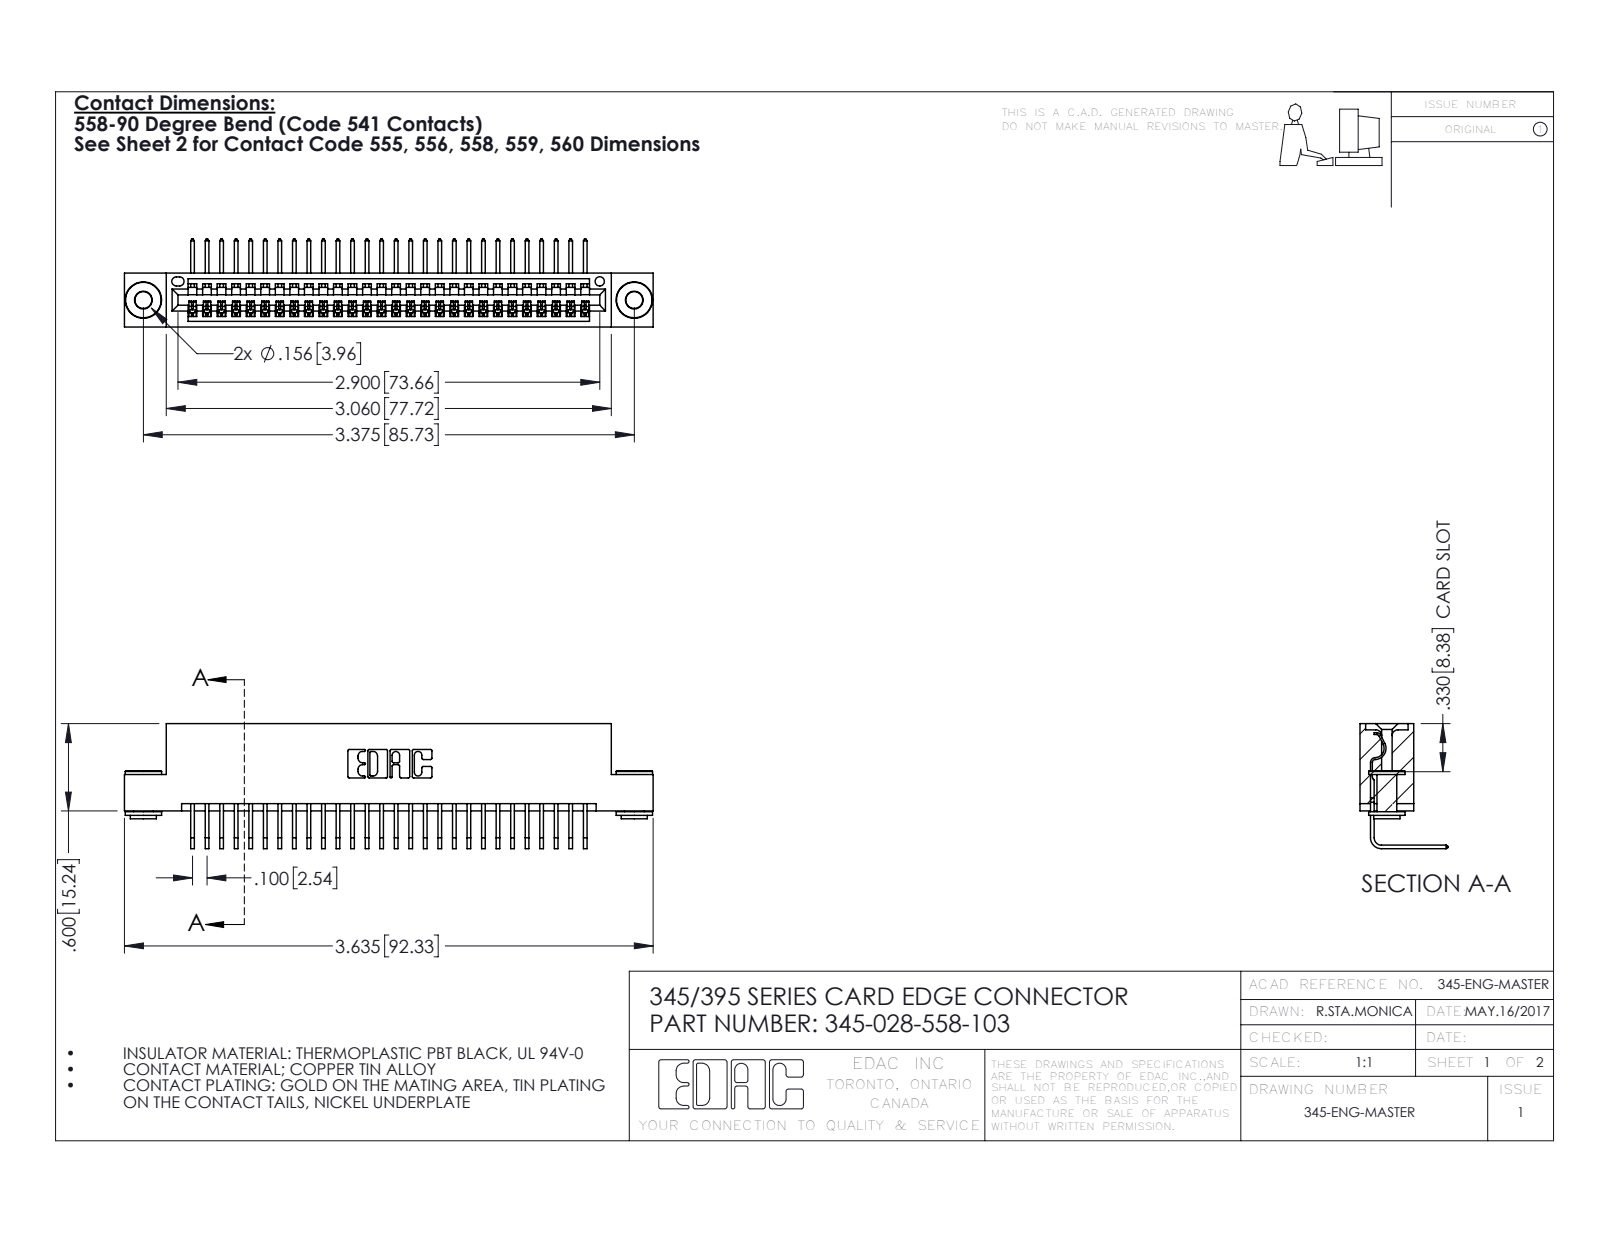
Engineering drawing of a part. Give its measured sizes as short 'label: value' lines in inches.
name: 345 Part_Flush Mounting Lugs - 0.156 Dia-TH; 345-292-001_558 Tail - 2; 345-250-002_345-250-002-102; 345-028-558-103
written by: SolidWorks 2016 (CONFIG_CONTROL_DESIGN)
unit: in
bodies: 31 solids, 1844 faces (1266 planar, 570 cylindrical, 8 other)
size: 3.635 × 0.859 × 0.605
volume: 0.535 in³; area: 18.95 in²
holes: 2× ⌀0.116, 2× ⌀0.156, 1× ⌀0.064
bosses: 2× ⌀0.25, 2× ⌀0.18, 2× ⌀0.136
rounds: 56× R0.006, 22× R0.01, 6× R0.007, 6× R0.031, 3× R0.026, 2× R0.031, 2× R0.04, 1× R0.014
face distances: 0.072, 0.298, 0.2, 0.37, 0.025, 0.098, 0.272, 0.225, 0.149, 0.072
hole spacings: 0.27, 3.14, 3.375
